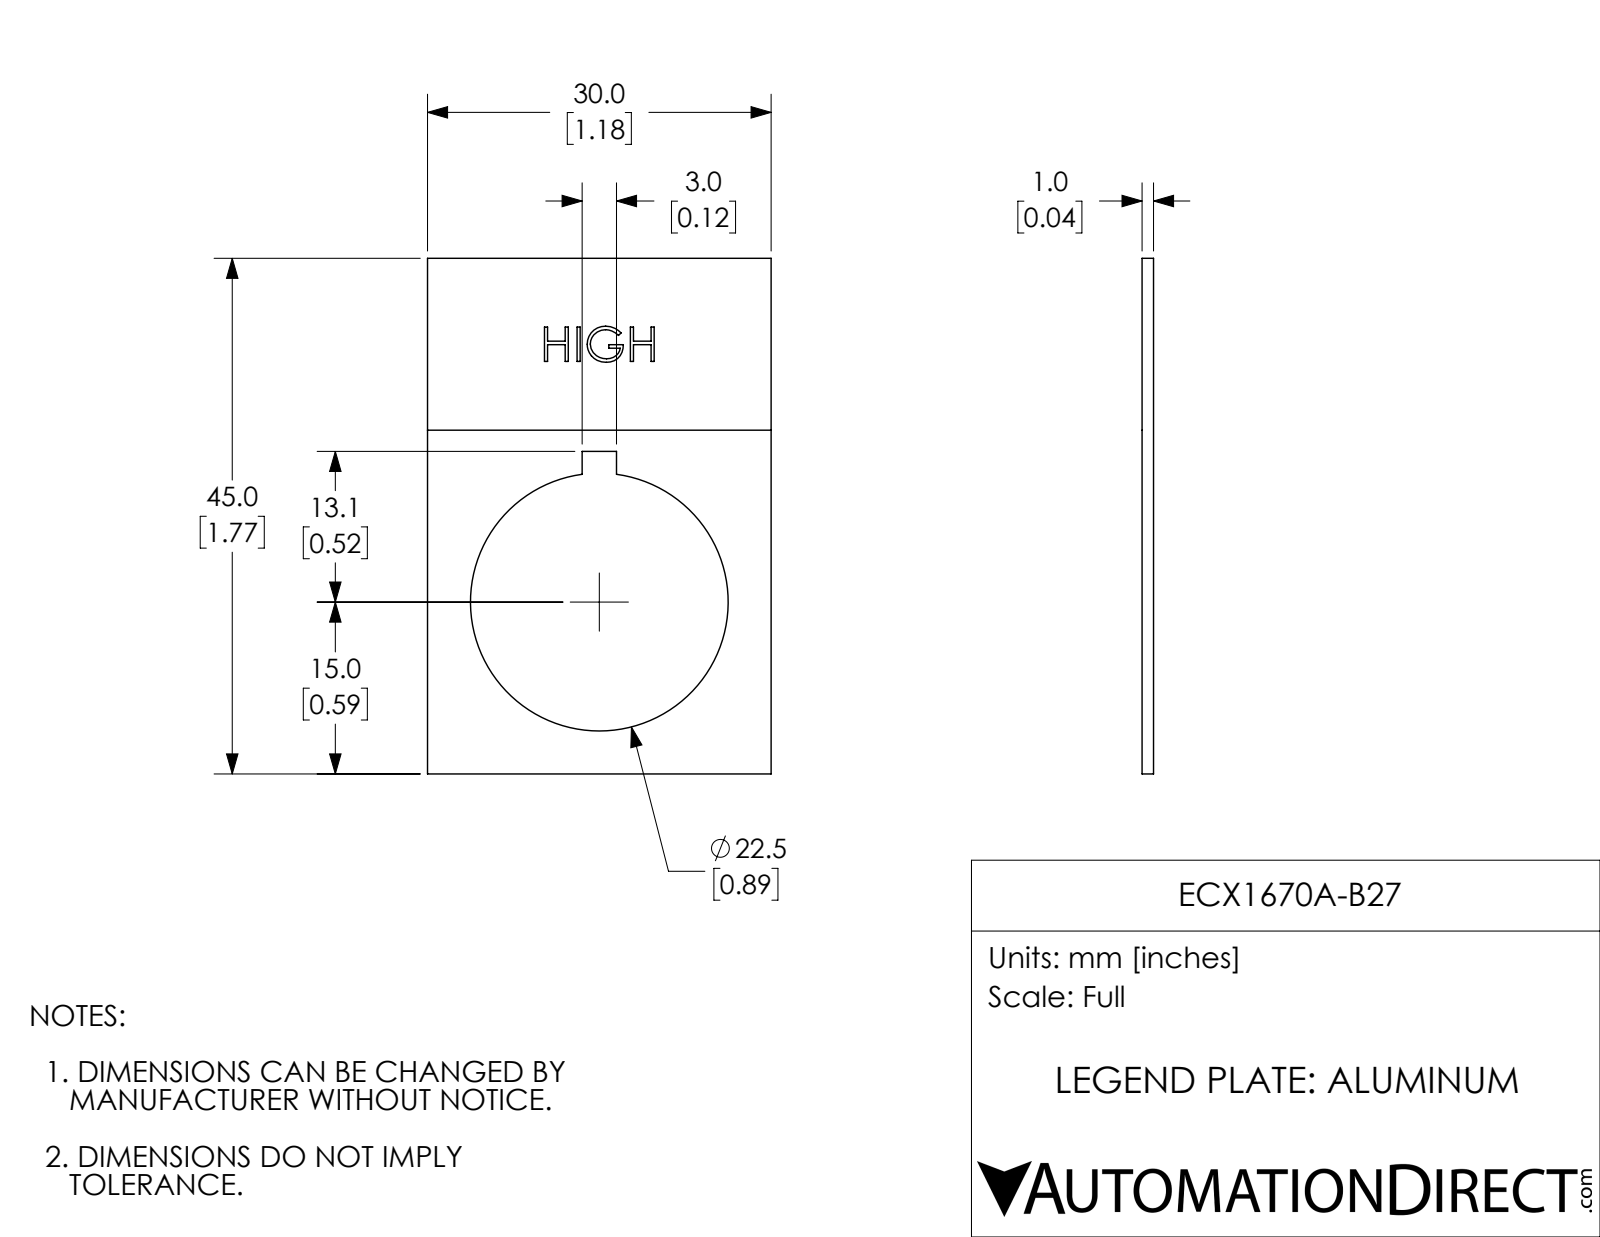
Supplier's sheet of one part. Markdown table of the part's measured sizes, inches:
| quantity | value |
| --- | --- |
| part name | ECX1670A-B27 |
| STEP written by | SolidWorks 2017 (AUTOMOTIVE_DESIGN) |
| units | inches |
| bodies | 1 solid, 58 faces (46 planar, 3 cylindrical, 9 other) |
| overall size | 1.772 × 1.181 × 0.039 |
| volume | 0.058 in³ |
| surface area | 3.285 in² |
| round holes (diameter × count) | 0.886 × 1 |
| main face-to-face distances | 0.039, 1.181, 1.772, 0.038, 0.531, 0.65, 1.108, 0.663, 0.118, 0.295 |
